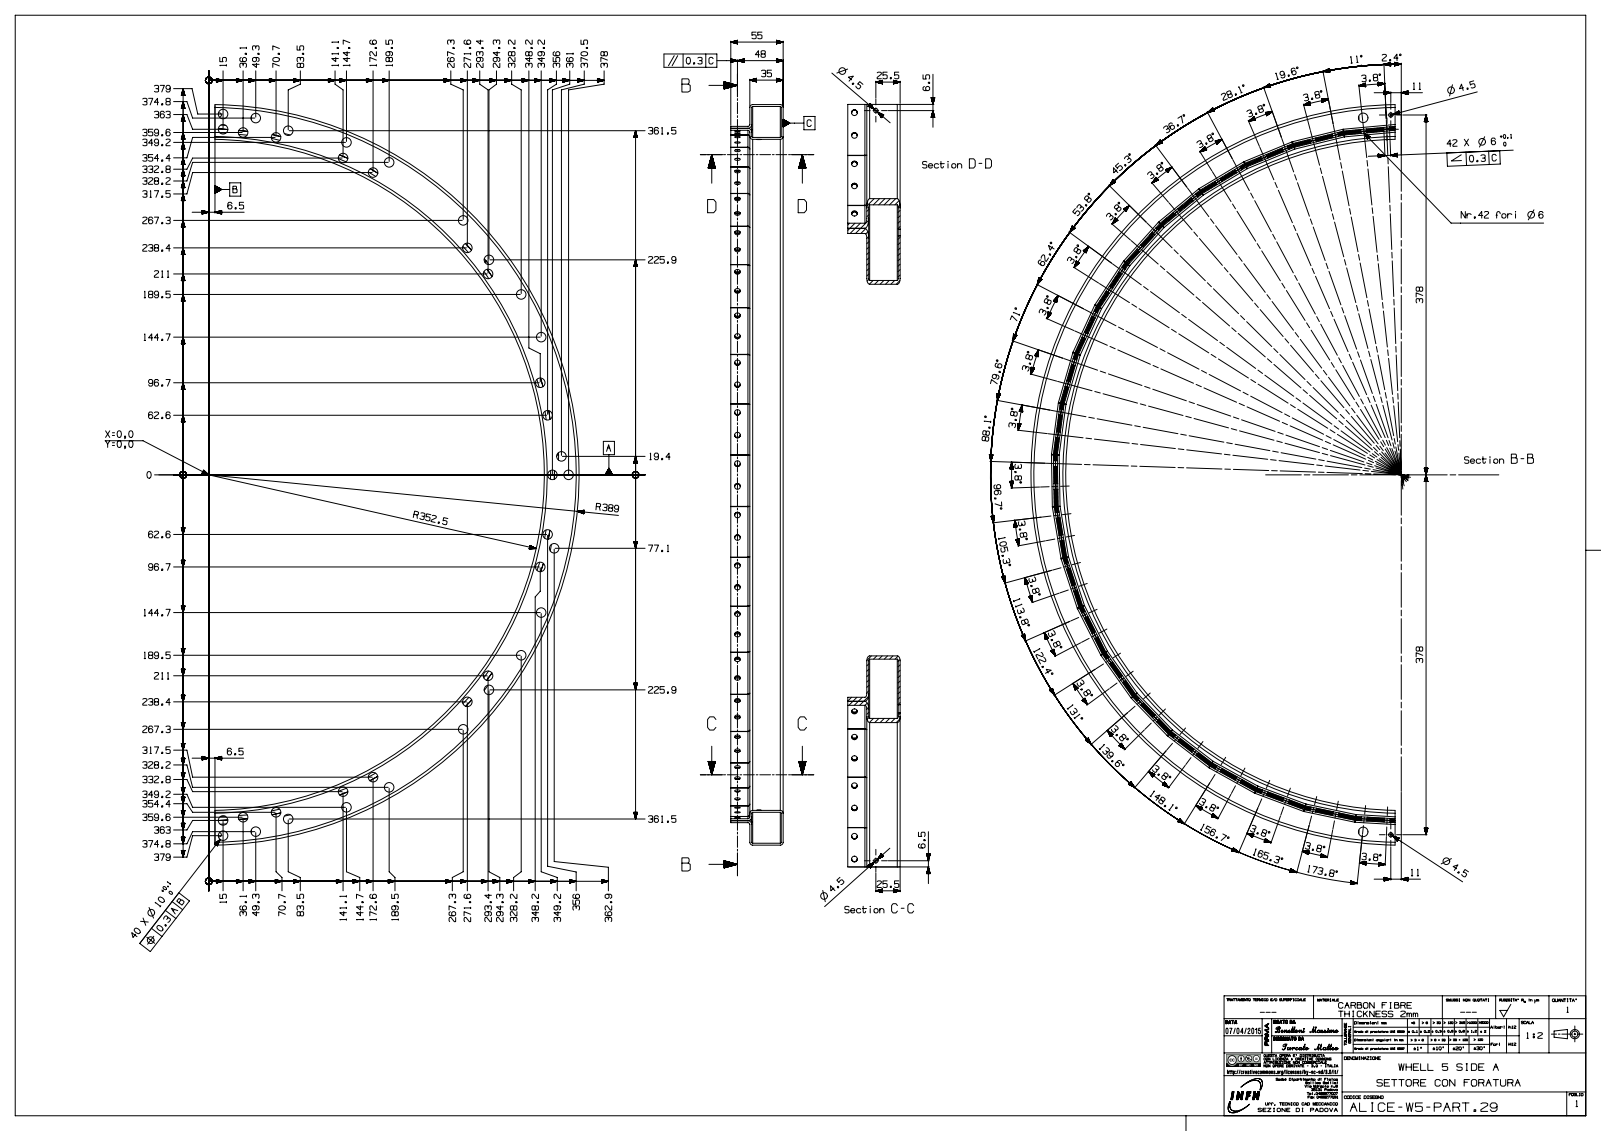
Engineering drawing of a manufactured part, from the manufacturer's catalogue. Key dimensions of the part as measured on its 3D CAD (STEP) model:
Part name (STEP PRODUCT): turc17C413856an6
STEP written by: SIEMENS PLM Software NX 8.5 (AP203_CONFIGURATION_CONTROLLED_3D_DESIGN_OF_MECHANICAL_PARTS_AND_ASSEMBLIES_MIM_LF)
Units: millimetres
Bodies: 1 solid, 480 faces (94 planar, 298 cylindrical, 88 other)
Overall size (bounding box): 777.89 × 382.5 × 55
Volume: 375 892 mm³ · Surface area: 387 028 mm²
Round holes (diameter × count): ⌀6 ×42, ⌀10 ×42, ⌀4.5 ×3
Partial cylindrical surfaces — rounded edges, fillets, slot ends (radius × count): R4 ×82, R2 ×62, R4.1 ×20, R352.5 ×1, R354.5 ×1, R387 ×1, R389 ×1
Main face-to-face distances: 2, 33, 2.1, 31, 35, 4.1, 55, 53, 22, 20
Hole centre spacings: 161.07, 35, 449.98, 49.53, 98.81, 126.76, 147.49, 156.63
